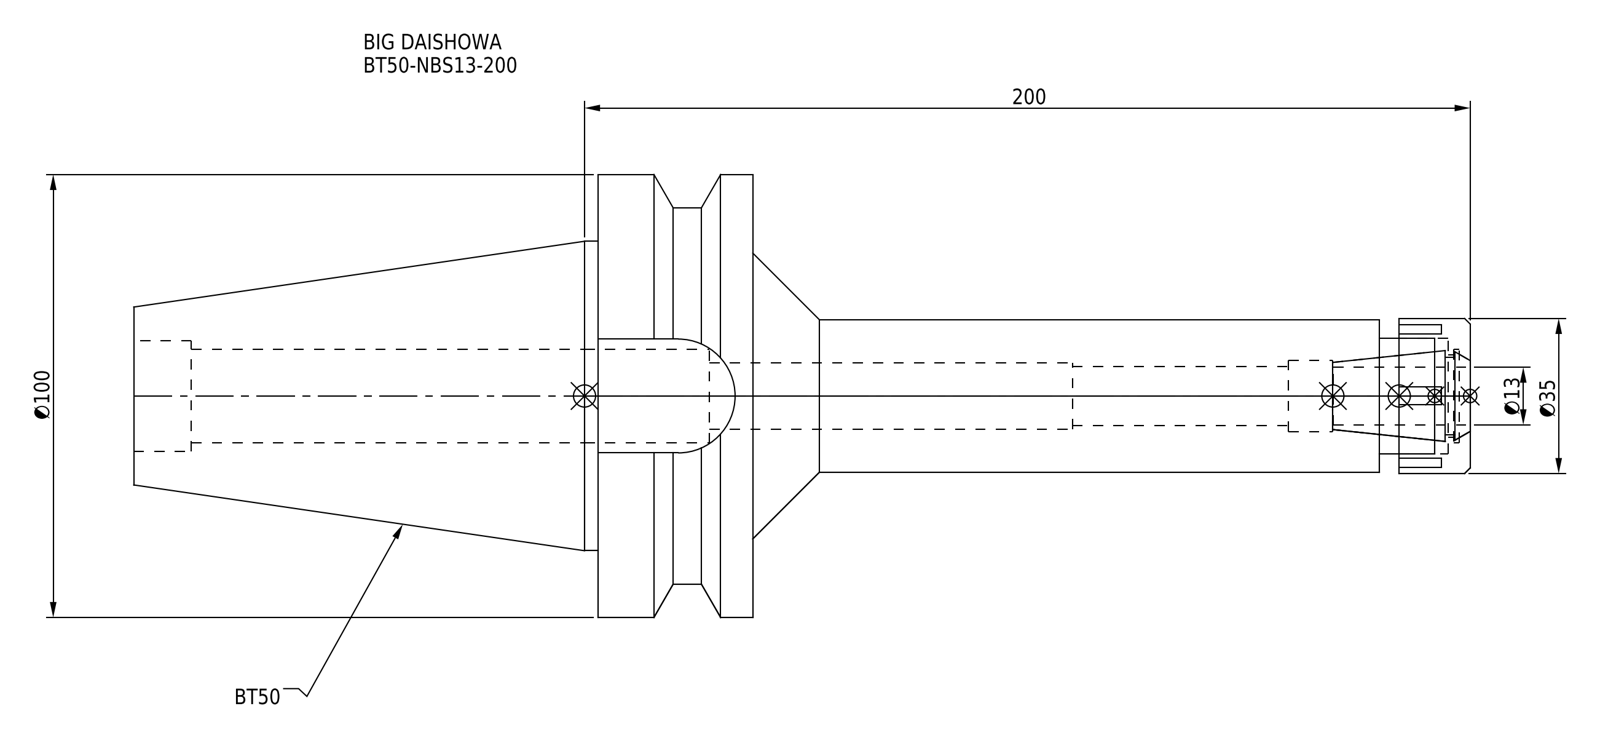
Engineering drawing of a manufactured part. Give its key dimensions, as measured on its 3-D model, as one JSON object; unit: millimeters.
{"part_name": "BT50NB13200-130_ASM.stp; DXF_TEMP_ASSY_ASM_4_ASM.stp; BT50-NBS13-200.stp; BT50-NBS13-200-FreeParts (+3 more)", "step_written_by": "SolidWorks 2019 (CONFIG_CONTROL_DESIGN)", "units": "millimeters", "bodies": {"solids": 2, "faces": 93, "planar": 45, "cylindrical": 34, "other": 14}, "overall_size": [301.8, 100, 100], "volume_mm3": 579636, "surface_area_mm2": 81718, "round_holes": [[13.3, 1], [15, 1], [16, 1], [18.5, 1], [21, 1], [21.2, 1], [25, 1], [26, 1]], "round_bosses_or_shafts": [[100, 1], [85, 1], [69.85, 1], [35, 1], [34.5, 1]], "partial_cylinders_radius": [[12.85, 1]], "face_to_face_distances": [35, 139.8, 104.8, 70.8, 162, 197, 301.8, 20.5, 8, 25.7]}
